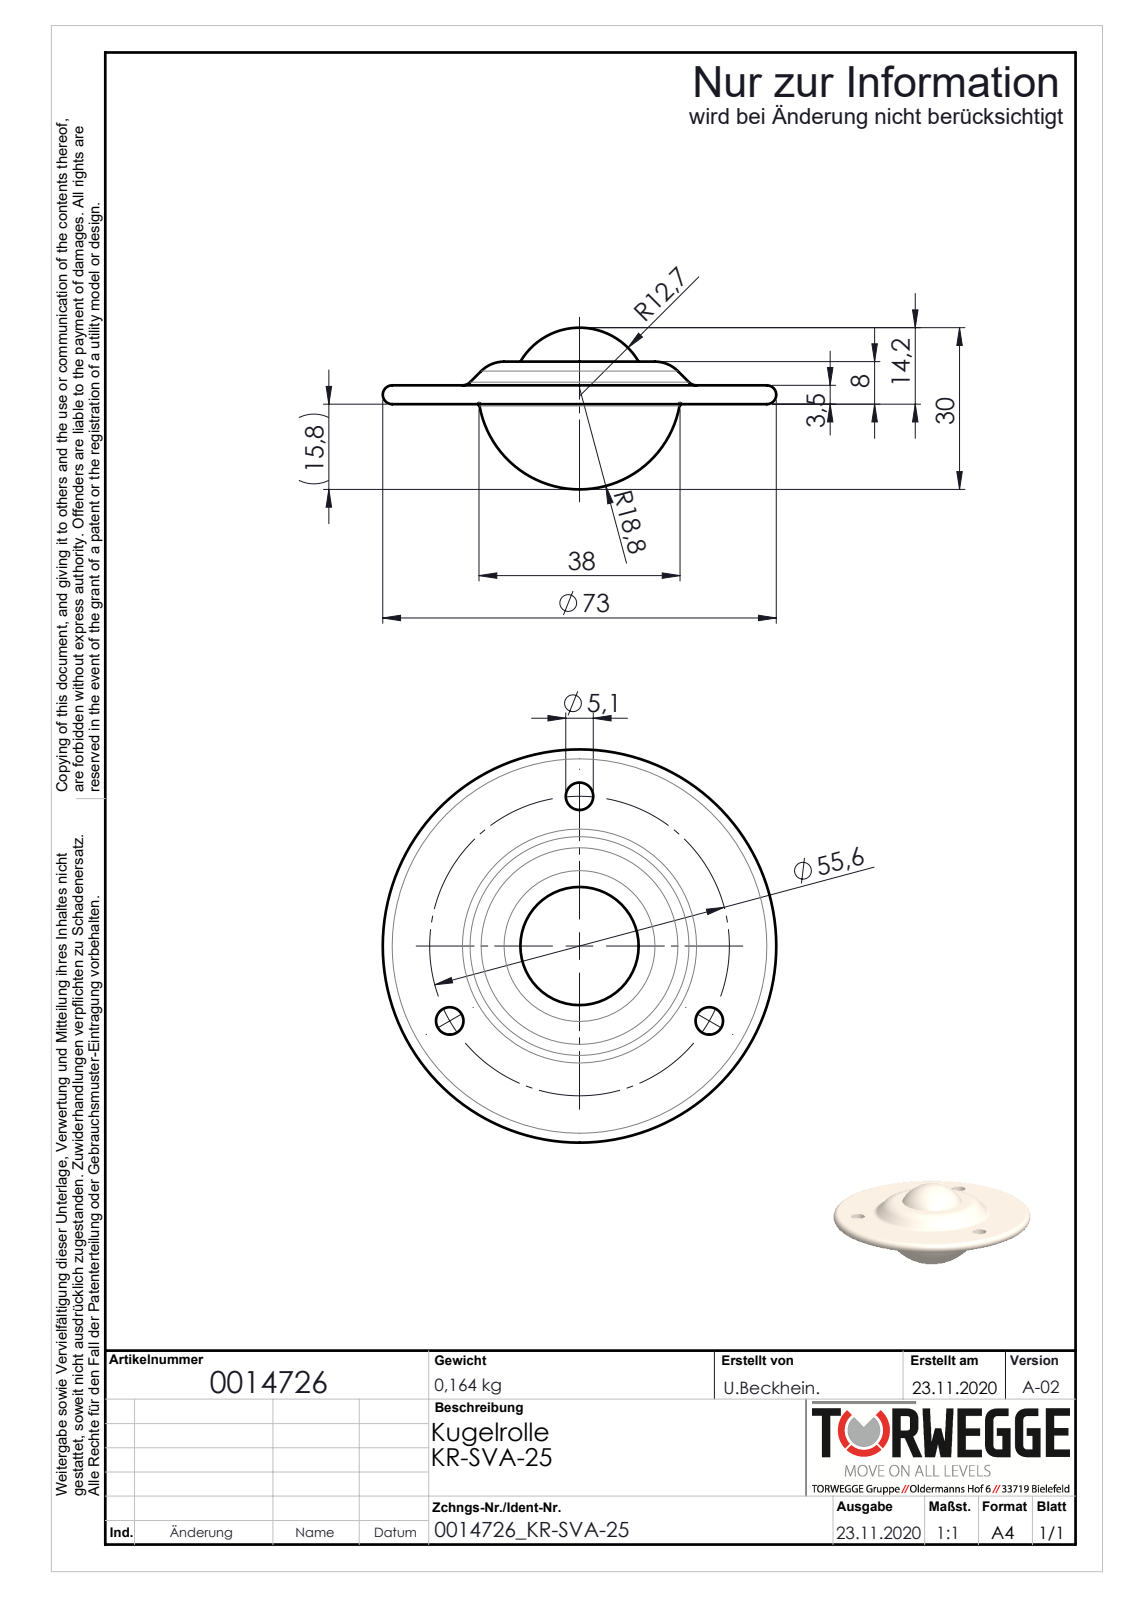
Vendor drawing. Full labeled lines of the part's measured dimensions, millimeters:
Part name (STEP PRODUCT): 0014726
STEP written by: SolidWorks 2018 (AUTOMOTIVE_DESIGN)
Units: millimetres
Bodies: 1 solid, 27 faces (4 planar, 8 cylindrical, 15 other)
Overall size (bounding box): 73 × 73 × 29.85
Volume: 29 029 mm³ · Surface area: 10 137 mm²
Round holes (diameter × count): ⌀5.1 ×3, ⌀64.8 ×1
Main face-to-face distances: 2.6, 0.9, 3.5, 7.9, 7, 4.4
Hole centre spacings: 27.8, 48.15, 48.16
